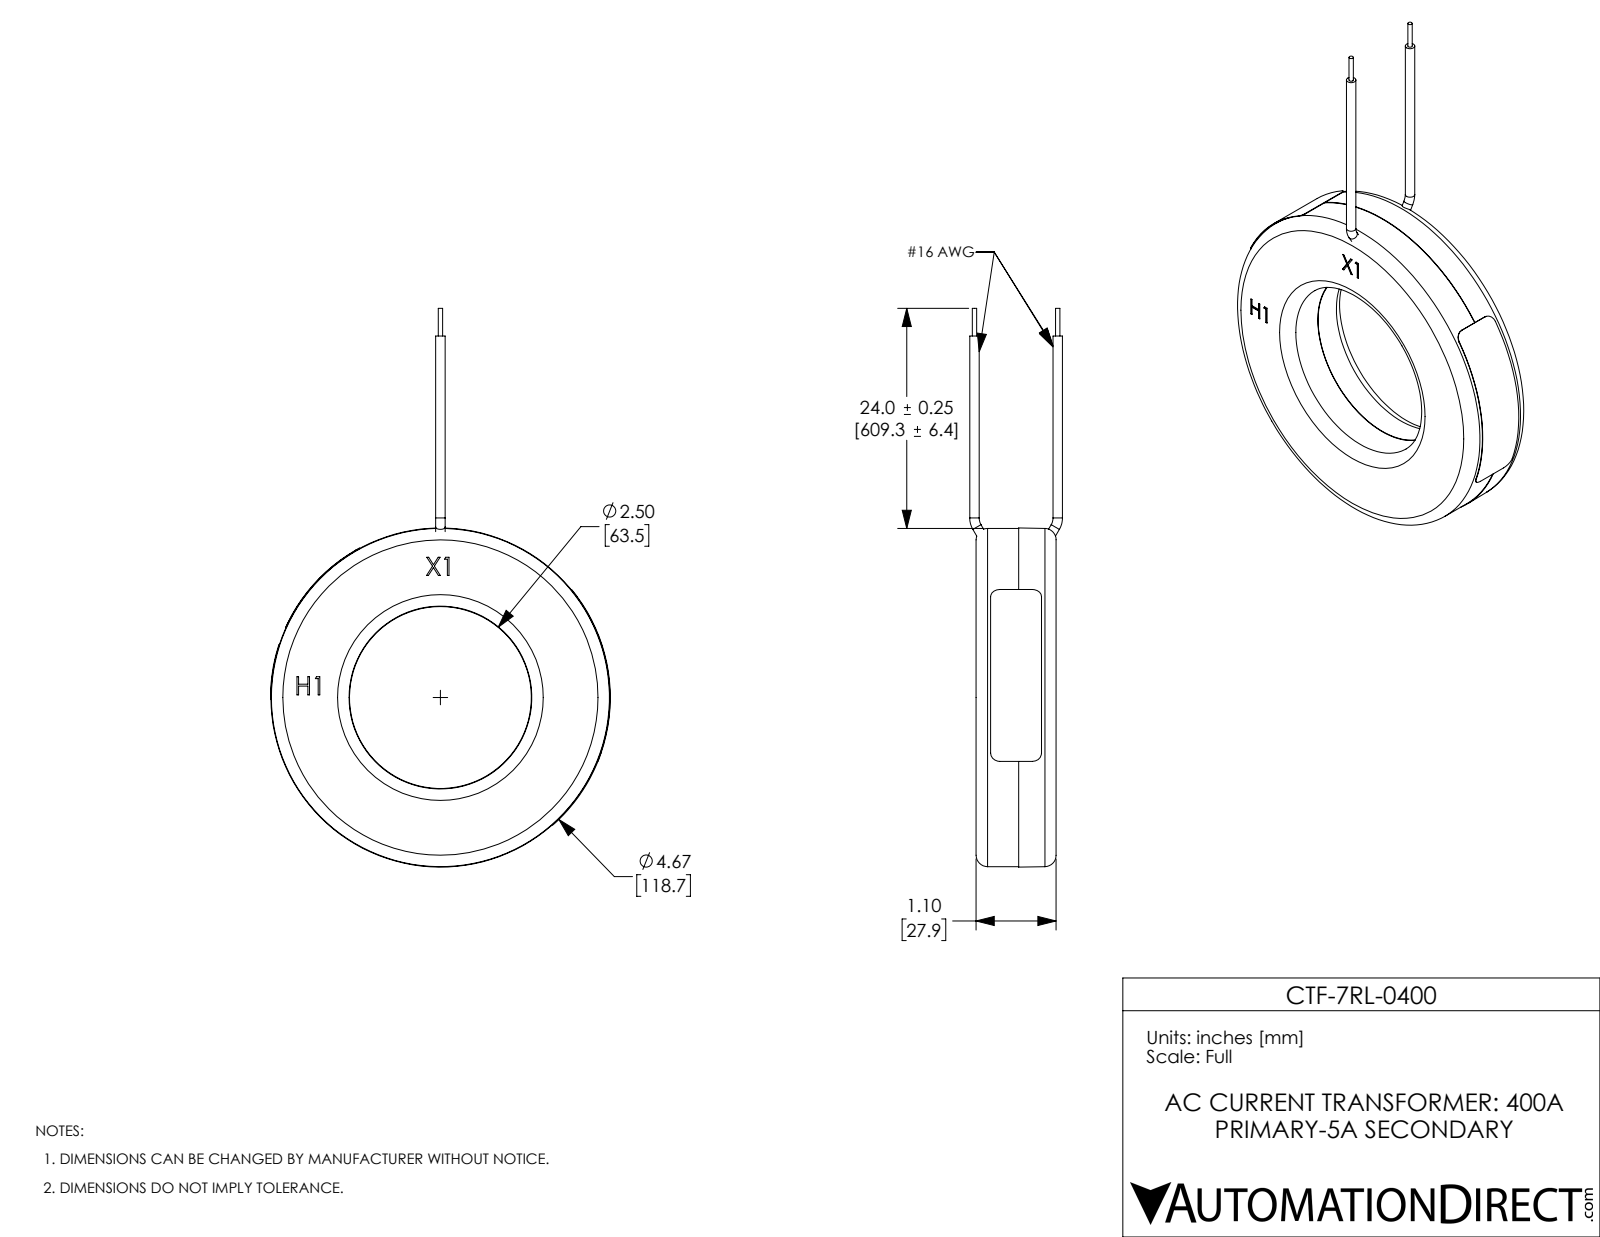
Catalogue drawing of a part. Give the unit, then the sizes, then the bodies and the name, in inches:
Units: inches
Overall size (bounding box): 7.679 × 4.673 × 1.275
Round holes (diameter × count): ⌀2.513 ×1
Round bosses / shafts (diameter × count): ⌀0.13 ×4, ⌀0.06 ×2, ⌀4.648 ×1
Partial cylindrical surfaces — rounded edges, fillets, slot ends (radius × count): R0.06 ×4, R0.125 ×4, R2.33 ×1, R2.33 ×1, R2.331 ×1, R2.336 ×1
Main face-to-face distances: 0.515, 1.1, 0.585, 1.09, 0.575, 0.2, 0.9, 0.315, 0.89, 0.7
Volume: 13.1 in³ · Surface area: 79.58 in²
Bodies: 6 solids, 114 faces (62 planar, 31 cylindrical, 21 other)
Part name (STEP PRODUCT): CTF-7RL-0400
STEP written by: SolidWorks 2018 (AUTOMOTIVE_DESIGN)
